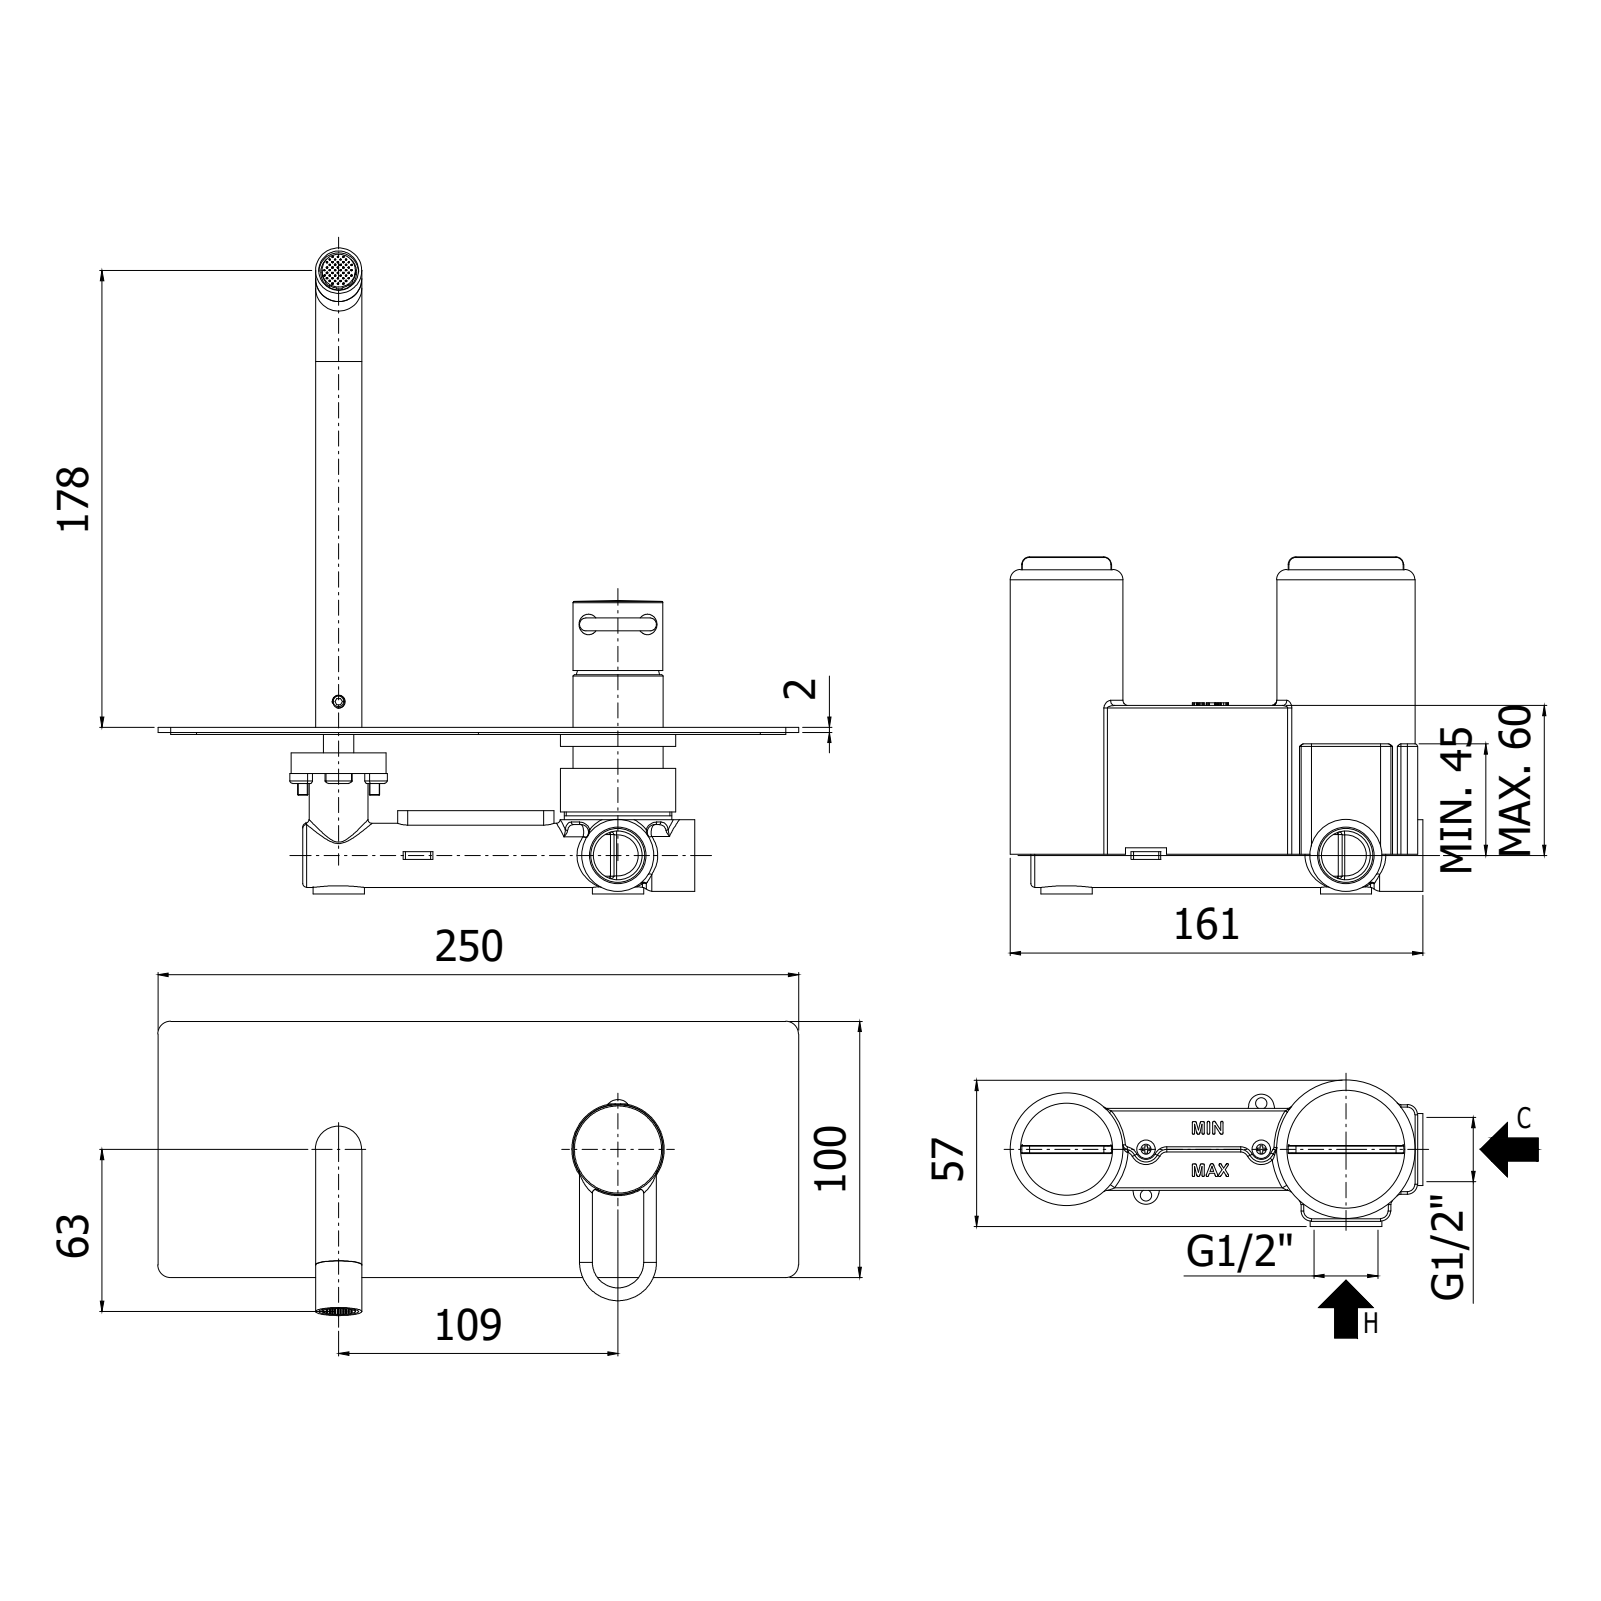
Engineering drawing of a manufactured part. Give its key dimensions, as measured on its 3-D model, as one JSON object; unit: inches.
{"part_name": "JK105CR", "step_written_by": "CREO PARAMETRIC BY PTC INC, 2020044 (CONFIG_CONTROL_DESIGN)", "units": "inches", "bodies": {"solids": 2, "faces": 184, "planar": 55, "cylindrical": 74, "other": 55}, "overall_size": [9.843, 7.444, 4.519], "volume_in3": 7.61, "surface_area_in2": 123.6, "round_holes": [[0.165, 2], [0.118, 1], [0.315, 1], [0.976, 1], [1.031, 1], [1.063, 1], [1.102, 1], [1.142, 1], [1.205, 1], [1.248, 1]], "round_bosses_or_shafts": [[0.709, 2], [0.197, 2], [1.386, 1], [1.378, 1], [0.299, 1], [0.217, 1]], "partial_cylinders_radius": [[0.039, 8], [0.118, 4], [0.197, 4], [0.02, 2], [0.059, 2], [0.138, 1], [0.687, 1]], "face_to_face_distances": [0.079, 3.937, 1.913, 1.835, 0.886, 0.098, 0.807, 1.028, 0.453, 9.843], "hole_center_spacings": [4.479]}
